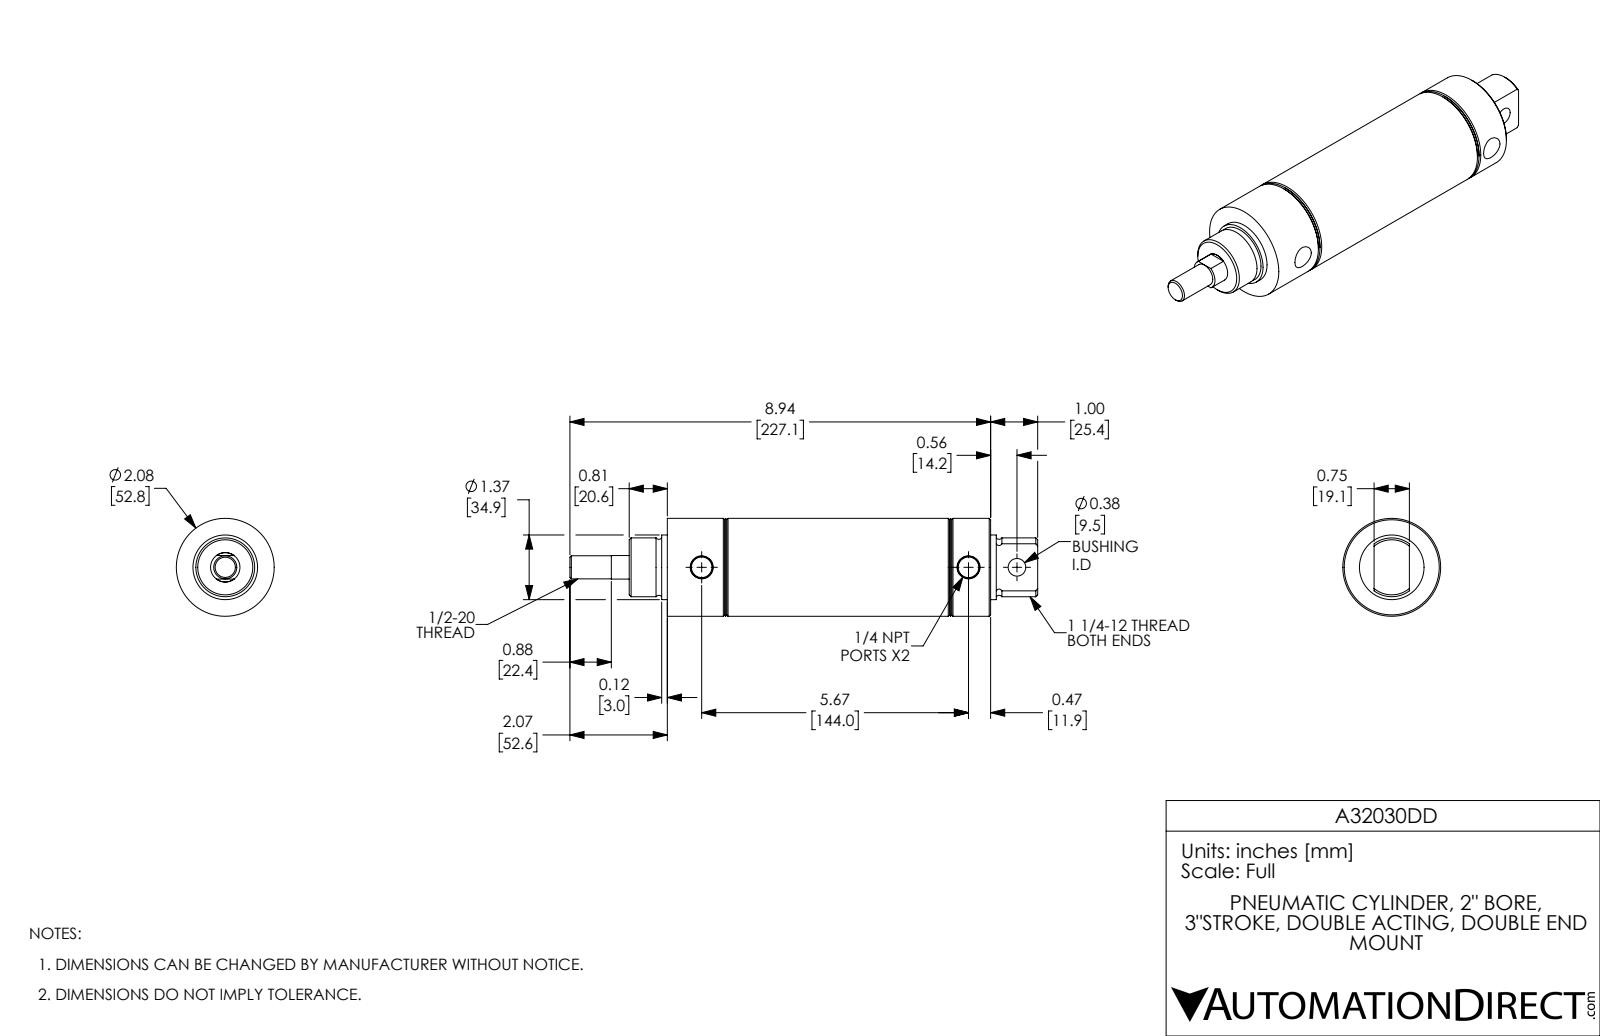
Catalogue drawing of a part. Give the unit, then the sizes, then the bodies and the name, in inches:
Units: inches
Overall size (bounding box): 9.94 × 2.08 × 2.08
Round holes (diameter × count): ⌀0.438 ×2, ⌀0.375 ×1, ⌀0.625 ×1, ⌀2 ×1
Round bosses / shafts (diameter × count): ⌀2.08 ×1, ⌀1.373 ×1, ⌀1.25 ×1, ⌀0.491 ×1
Main face-to-face distances: 1.685, 5.185, 0.5, 3.5, 3, 4.685, 2.185, 6.87, 0.12, 1.805
Hole centre spacings: 1.03, 5.67, 6.7
Volume: 16.67 in³ · Surface area: 116.6 in²
Bodies: 2 solids, 88 faces (20 planar, 30 cylindrical, 38 other)
Part name (STEP PRODUCT): A32030DD-Rod; A32030DD; A32030DD-MainBody
STEP written by: SolidWorks 2017 (AUTOMOTIVE_DESIGN)
